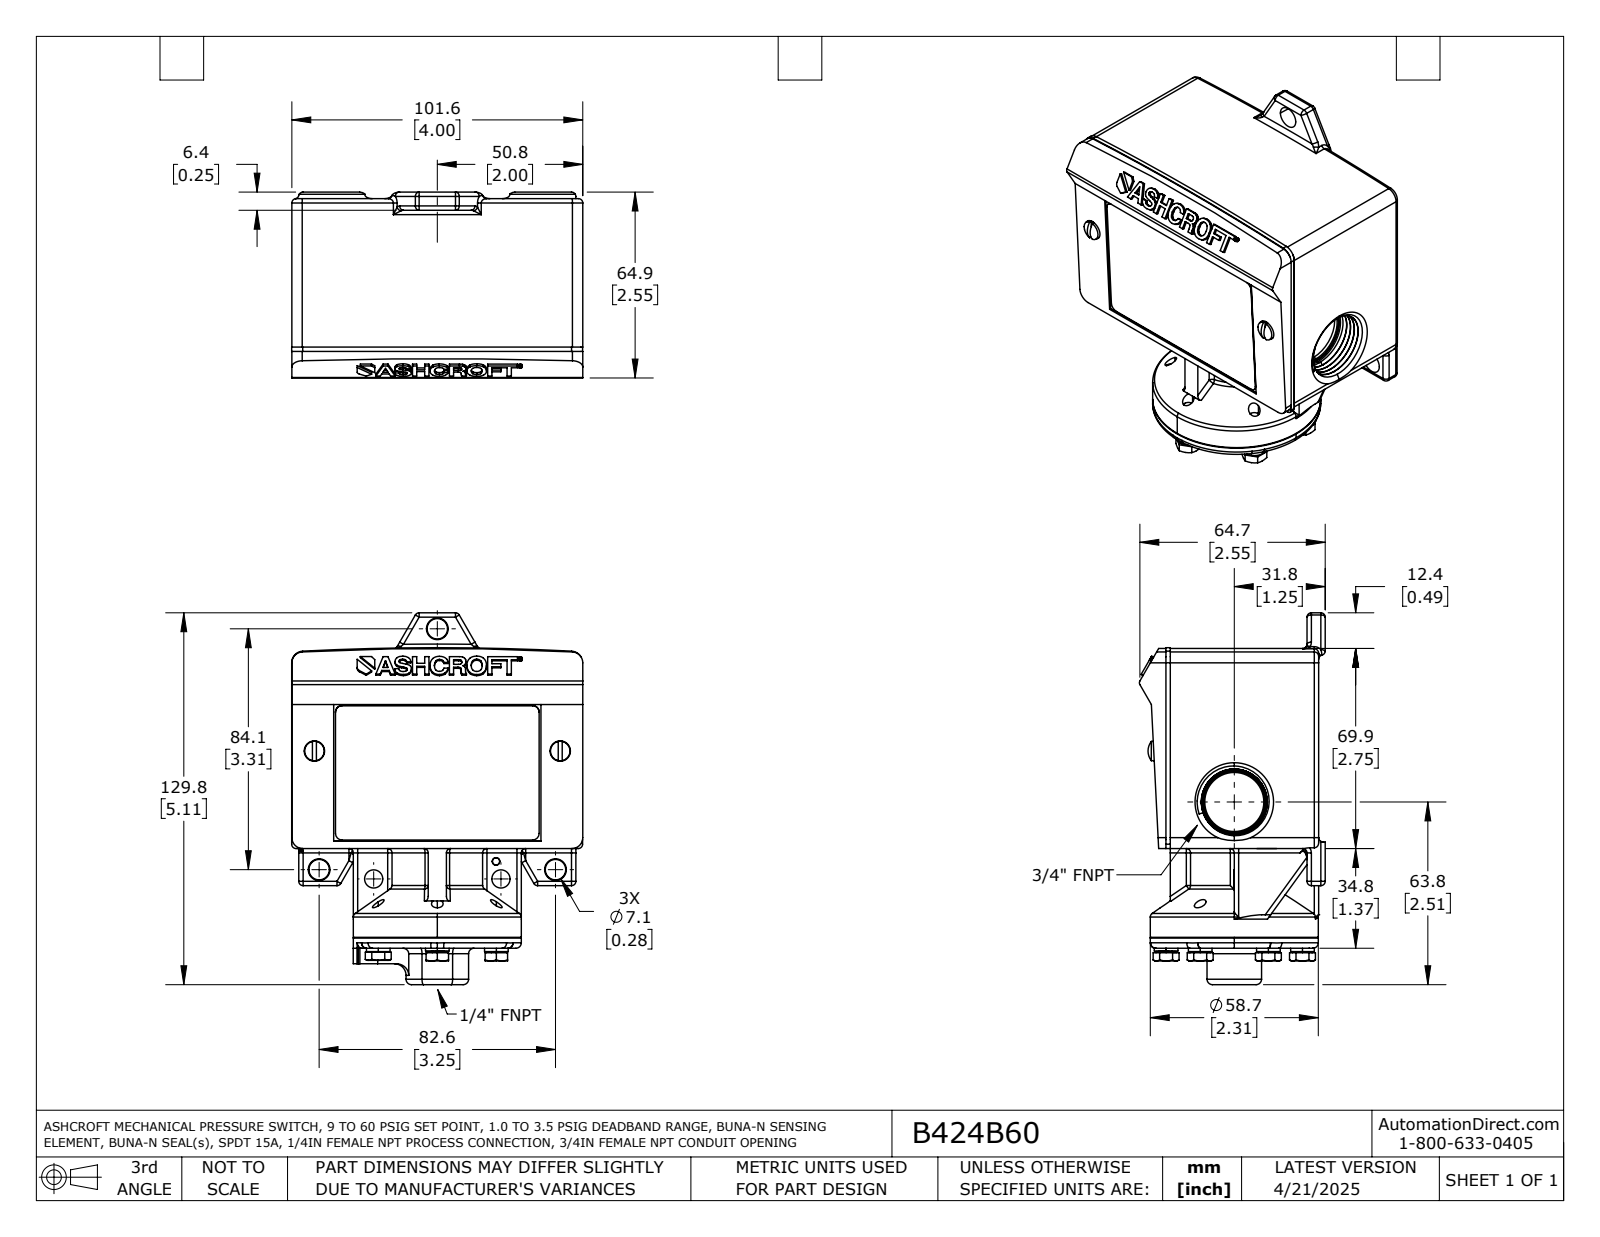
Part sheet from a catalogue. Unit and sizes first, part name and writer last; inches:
Units: inches
Overall size (bounding box): 5.111 × 4.003 × 2.555
Round holes (diameter × count): ⌀0.161 ×6, ⌀0.192 ×5, ⌀0.209 ×5, ⌀0.187 ×4, ⌀0.28 ×2, ⌀0.455 ×1, ⌀0.812 ×1
Round bosses / shafts (diameter × count): ⌀0.325 ×6, ⌀0.278 ×6, ⌀0.19 ×5, ⌀0.27 ×2, ⌀0.25 ×2, ⌀2.31 ×1
Partial cylindrical surfaces — rounded edges, fillets, slot ends (radius × count): R0.06 ×92, R0.03 ×5, R0.075 ×4, R0.09 ×4, R0.15 ×4, R0.01 ×2, R0.094 ×2, R0.16 ×2
Main face-to-face distances: 4, 0.015, 1.37, 0.09, 3.91, 0.44, 3.56, 3.47, 0.35, 0.845
Hole centre spacings: 0.937, 1.624, 1.875, 0.938, 3.38
Volume: 28.57 in³ · Surface area: 84.51 in²
Bodies: 2 solids, 1259 faces (345 planar, 472 cylindrical, 442 other)
Part name (STEP PRODUCT): B424B60
STEP written by: SolidWorks 2021 (AUTOMOTIVE_DESIGN)
